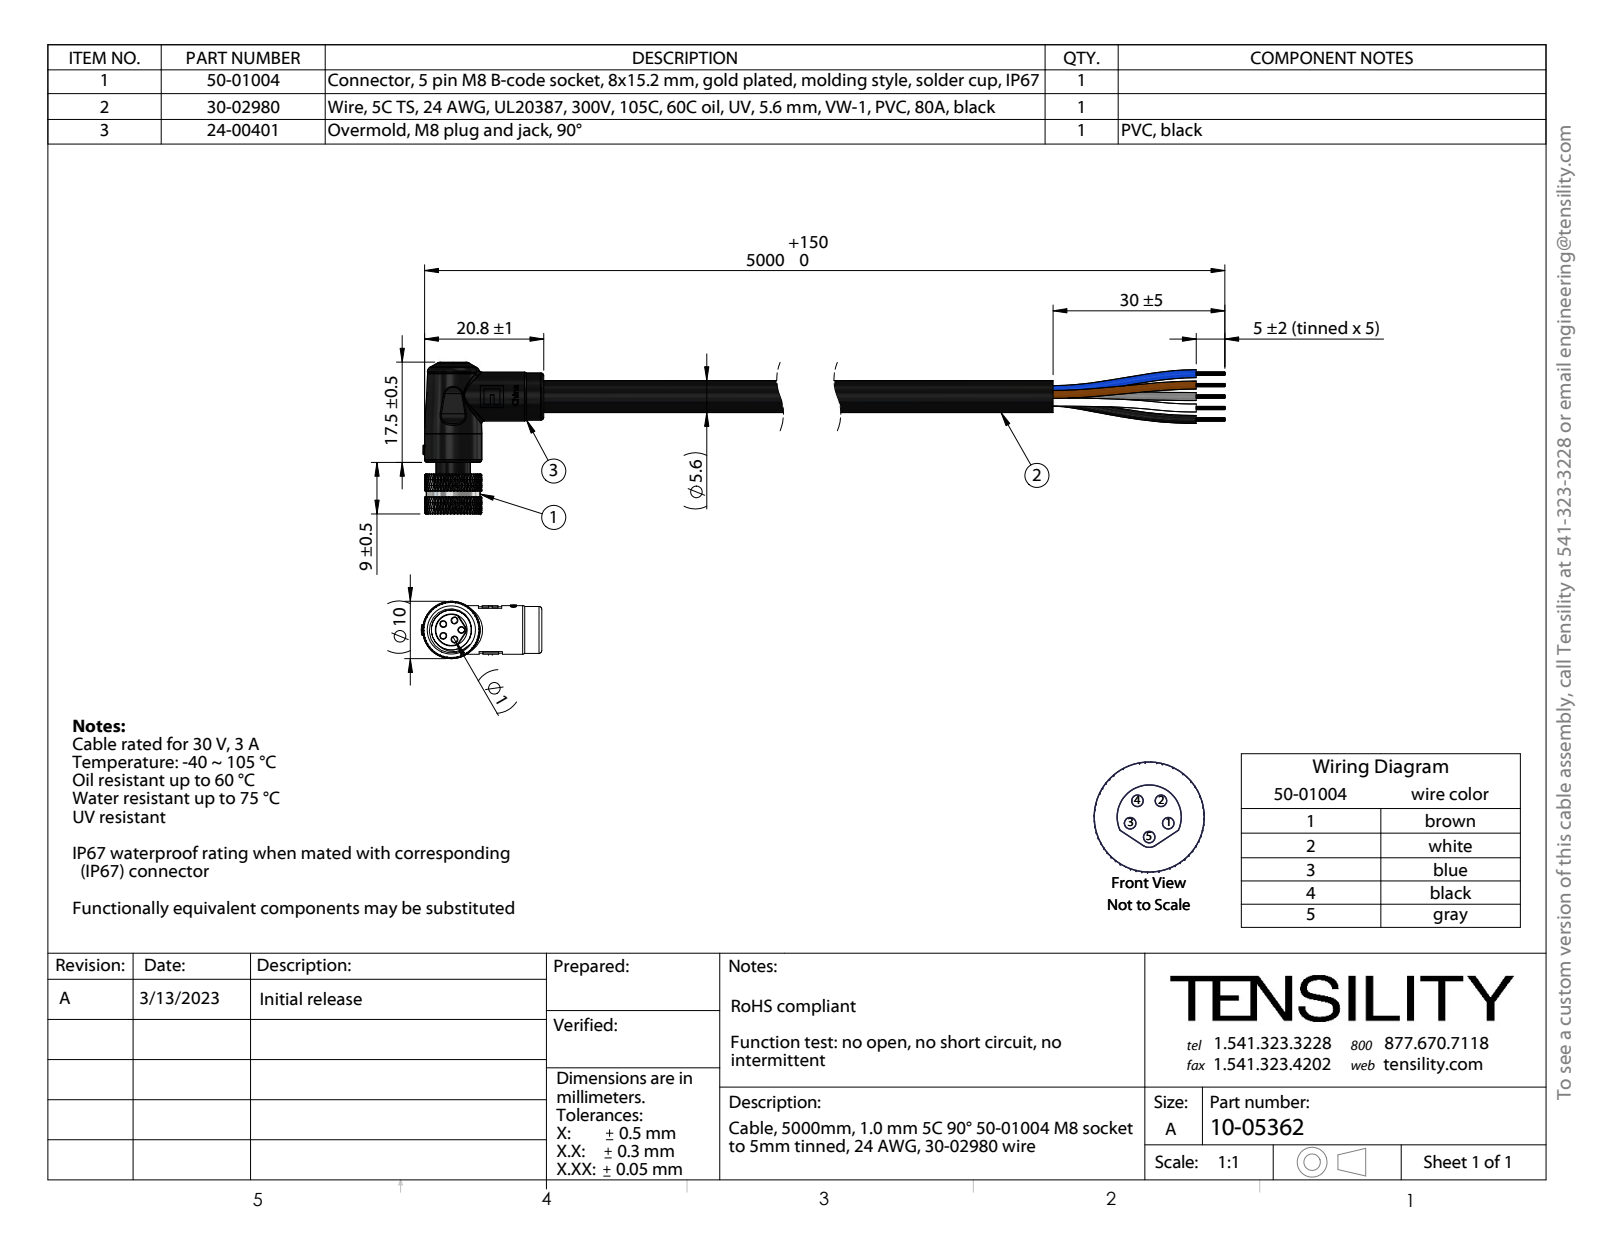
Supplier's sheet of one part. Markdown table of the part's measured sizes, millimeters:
| quantity | value |
| --- | --- |
| part name | 50-01004-02_STEP; 50-01004-01; 10-05359revA; 24-00401 (+4 more) |
| STEP written by | SolidWorks 2021 (CONFIG_CONTROL_DESIGN) |
| units | millimeters |
| bodies | 422 solids, 2597 faces (1029 planar, 1391 cylindrical, 177 other) |
| overall size | 201.05 × 26.5 × 10 |
| volume | 6 272 mm³ |
| surface area | 35 247 mm² |
| round holes (diameter × count) | 1.1 × 5, 1.2 × 5, 1.4 × 5, 3.82 × 1, 4.02 × 1, 6.3 × 1, 7 × 1 |
| round bosses / shafts (diameter × count) | 1.5 × 5, 10 × 1, 9.4 × 1, 9 × 1, 8.5 × 1, 8.2 × 1, 6.8 × 1, 6 × 1 |
| partial cylindrical surfaces (radius × count) | 0.1 × 12, 0.2 × 10, 0.4 × 10, 0.9 × 1, 2.8 × 1, 4.05 × 1, 4.25 × 1, 5 × 1 |
| main face-to-face distances | 2, 9, 7, 150, 2.5, 0.5, 1, 3.5, 1.5, 3.2 |
| hole center spacings | 0.35, 0.37, 0.32, 1.2, 1.41, 1.75, 2.28, 1.32 |
